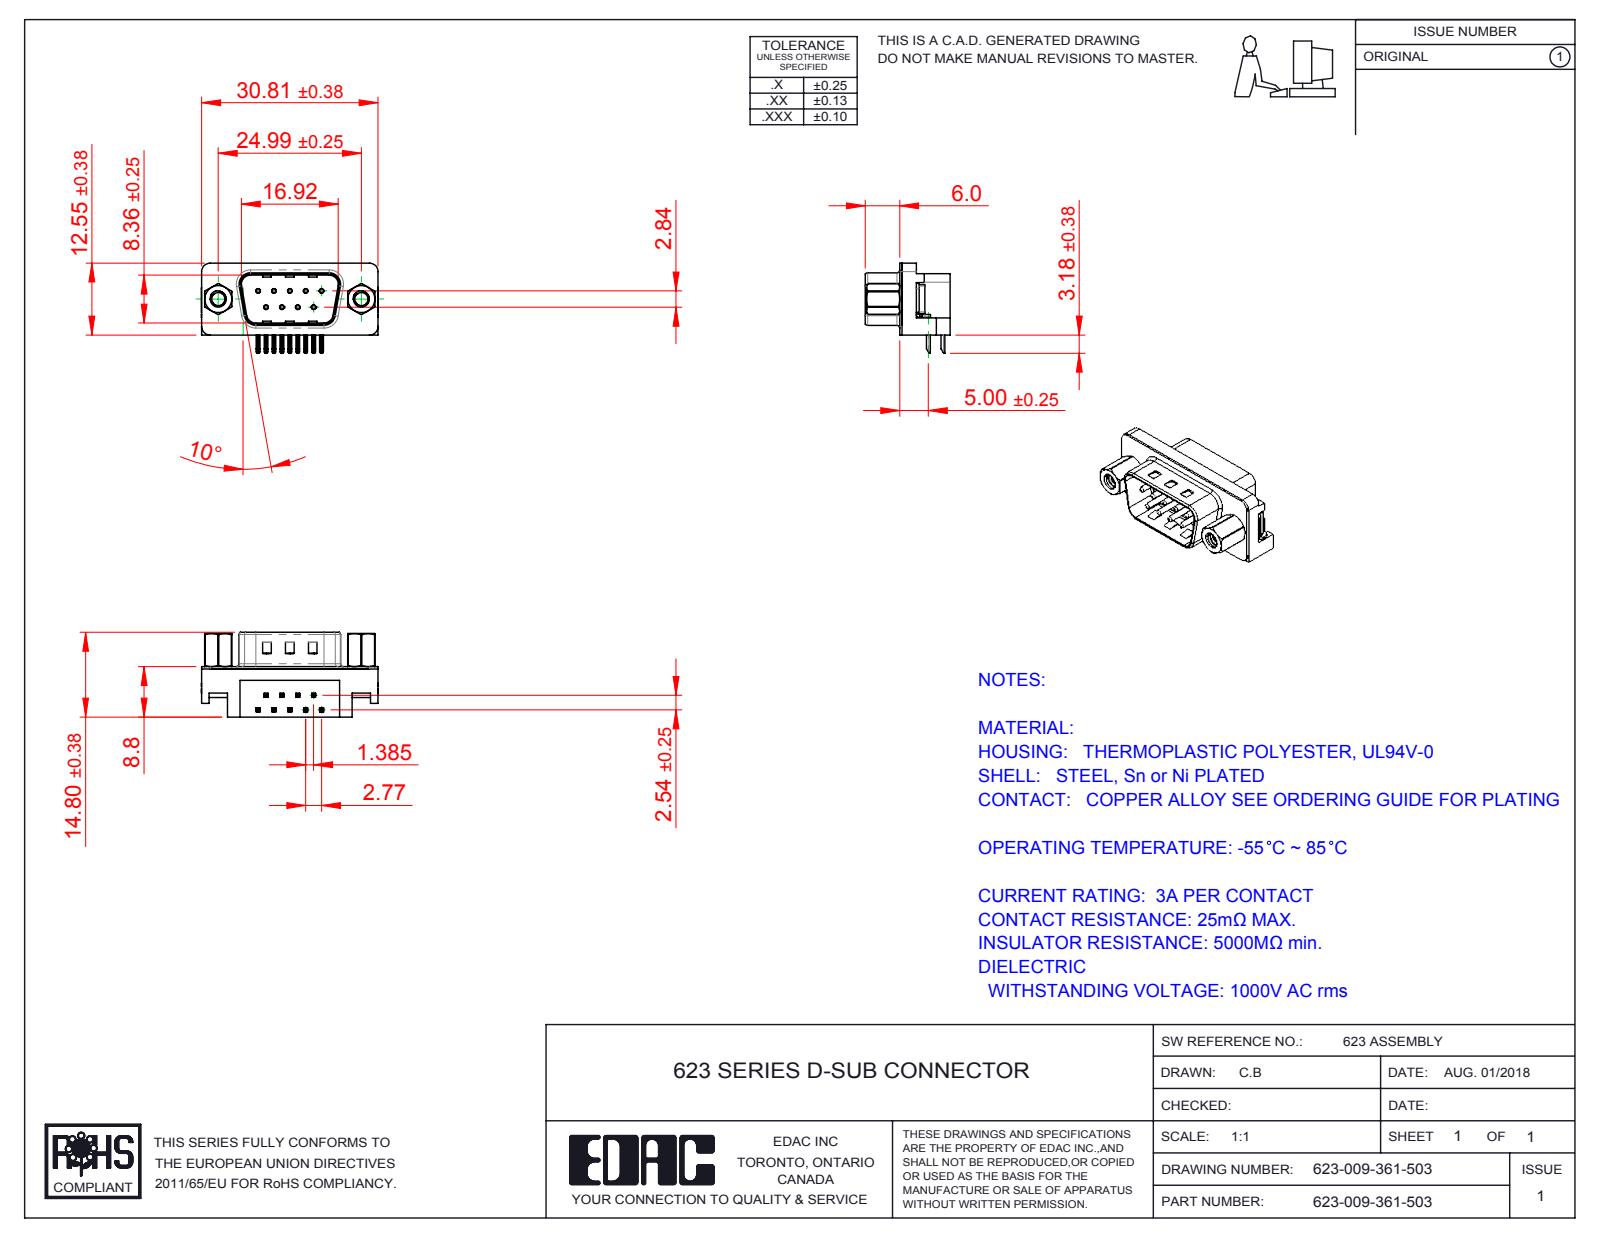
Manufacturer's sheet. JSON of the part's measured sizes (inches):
{"part_name": "623-009-361-503; 623 4-40 Threaded Rivet; 623 Non Board Mount; 623 Contact Bottom (+4 more)", "step_written_by": "SolidWorks 2016 (CONFIG_CONTROL_DESIGN)", "units": "inches", "bodies": {"solids": 17, "faces": 1105, "planar": 595, "cylindrical": 373, "other": 137}, "overall_size": [1.216, 0.619, 0.583], "volume_in3": 0.163, "surface_area_in2": 6.581, "round_holes": [[0.014, 9], [0.031, 9], [0.089, 2], [0.09, 2], [0.157, 2], [0.189, 2], [0.197, 2]], "round_bosses_or_shafts": [[0.03, 9], [0.193, 2], [0.187, 2], [0.154, 2], [0.11, 2]], "partial_cylinders_radius": [[0.01, 44], [0.005, 18], [0.039, 16], [0.02, 9], [0.059, 8], [0.035, 4], [0.063, 4], [0.079, 4]], "face_to_face_distances": [0.016, 0.331, 0.346, 0.232, 0.114, 0.098, 0.014, 0.345, 0.421, 0.407], "hole_center_spacings": [0.124, 0.109, 0.218, 0.198, 0.198, 0.327, 0.294, 0.295]}
